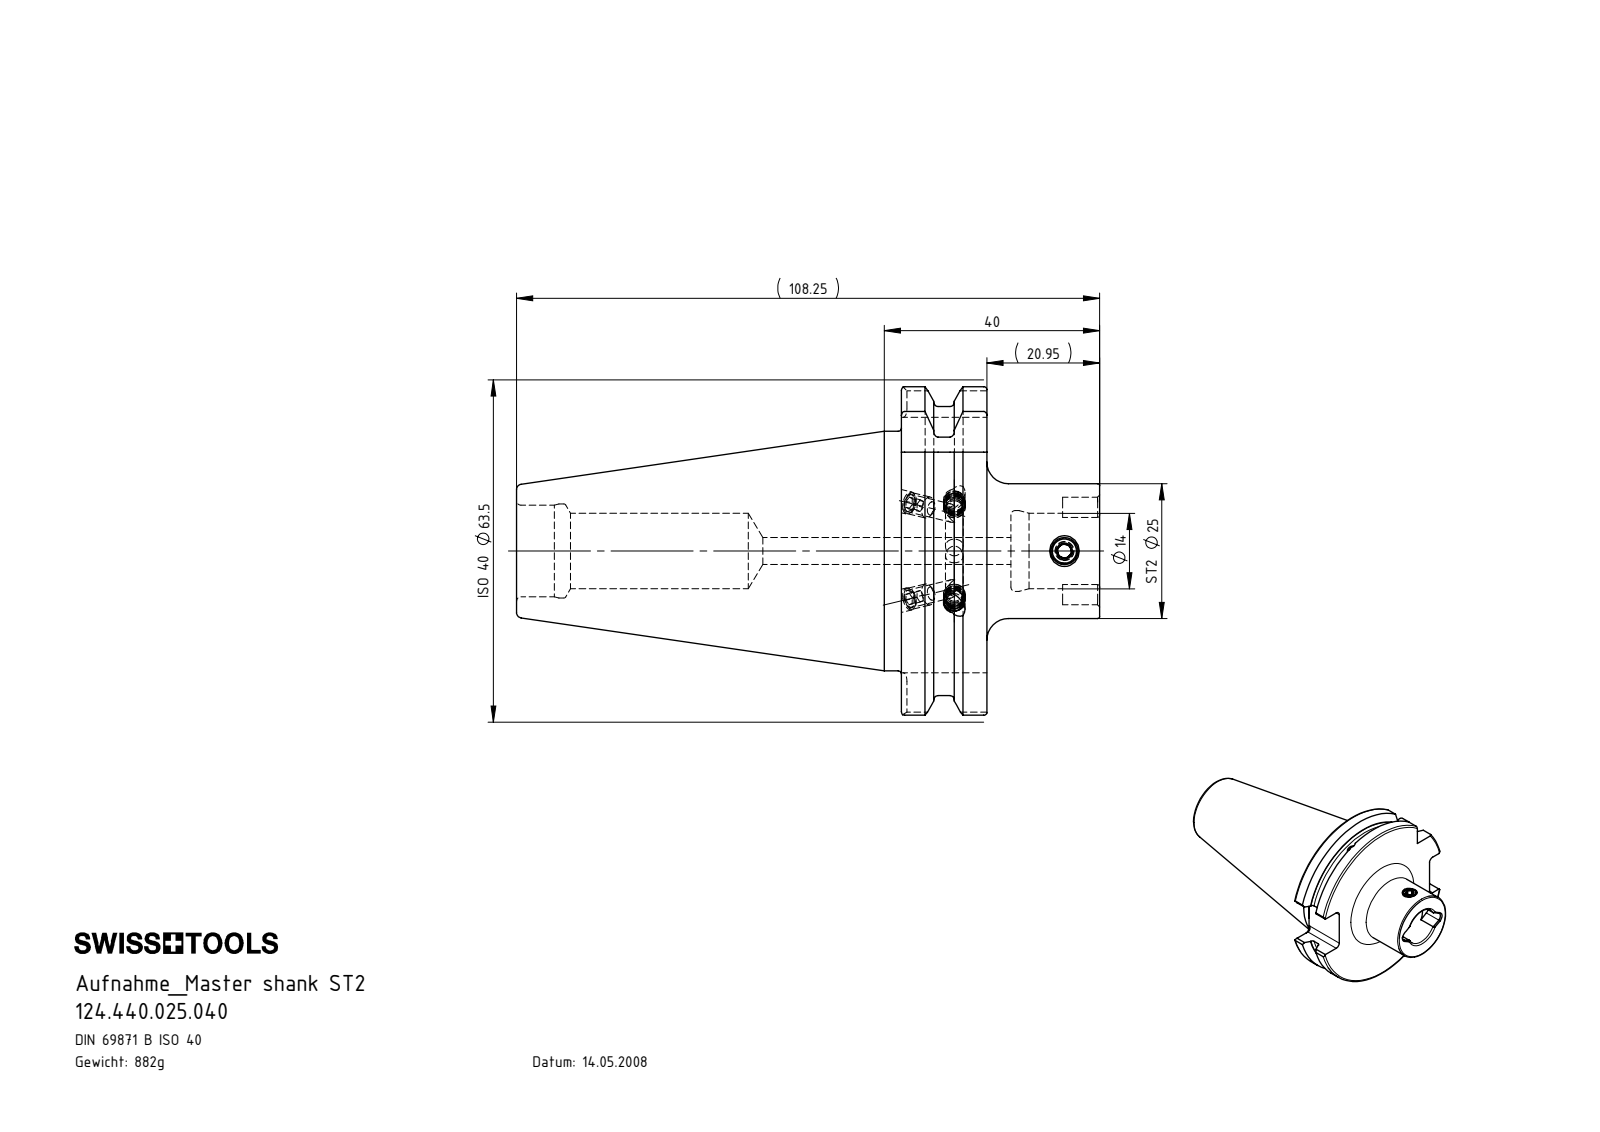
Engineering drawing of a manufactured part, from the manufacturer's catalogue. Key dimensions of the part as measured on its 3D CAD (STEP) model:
Part name (STEP PRODUCT): SB4-ST2.K01.040_B_mit Bundkhlung; SB4.ST2.K01.040; ISO 4026 - M4 x 5_PreviewCfg; ST2-ER1.001.006_A (+1 more)
STEP written by: SolidWorks 2017 (AUTOMOTIVE_DESIGN)
Units: millimetres
Bodies: 8 solids, 206 faces (78 planar, 50 cylindrical, 78 other)
Overall size (bounding box): 108.25 × 63.5 × 60.94
Volume: 112 339 mm³ · Surface area: 22 821 mm²
Round holes (diameter × count): ⌀3.3 ×3, ⌀3 ×2, ⌀4.2 ×2, ⌀2.5 ×1, ⌀4 ×1, ⌀4.5 ×1, ⌀5 ×1, ⌀14 ×1, ⌀15 ×1, ⌀17 ×1, ⌀17.45 ×1
Round bosses / shafts (diameter × count): ⌀4 ×4, ⌀44.45 ×1, ⌀25 ×1, ⌀5 ×1
Partial cylindrical surfaces — rounded edges, fillets, slot ends (radius × count): R1.6 ×8, R1.8 ×2, R28 ×1, R31.75 ×1
Main face-to-face distances: 15.85, 36.8, 20.95, 47.4, 71.45, 87.3, 108.25, 4.45, 91.75, 20.3
